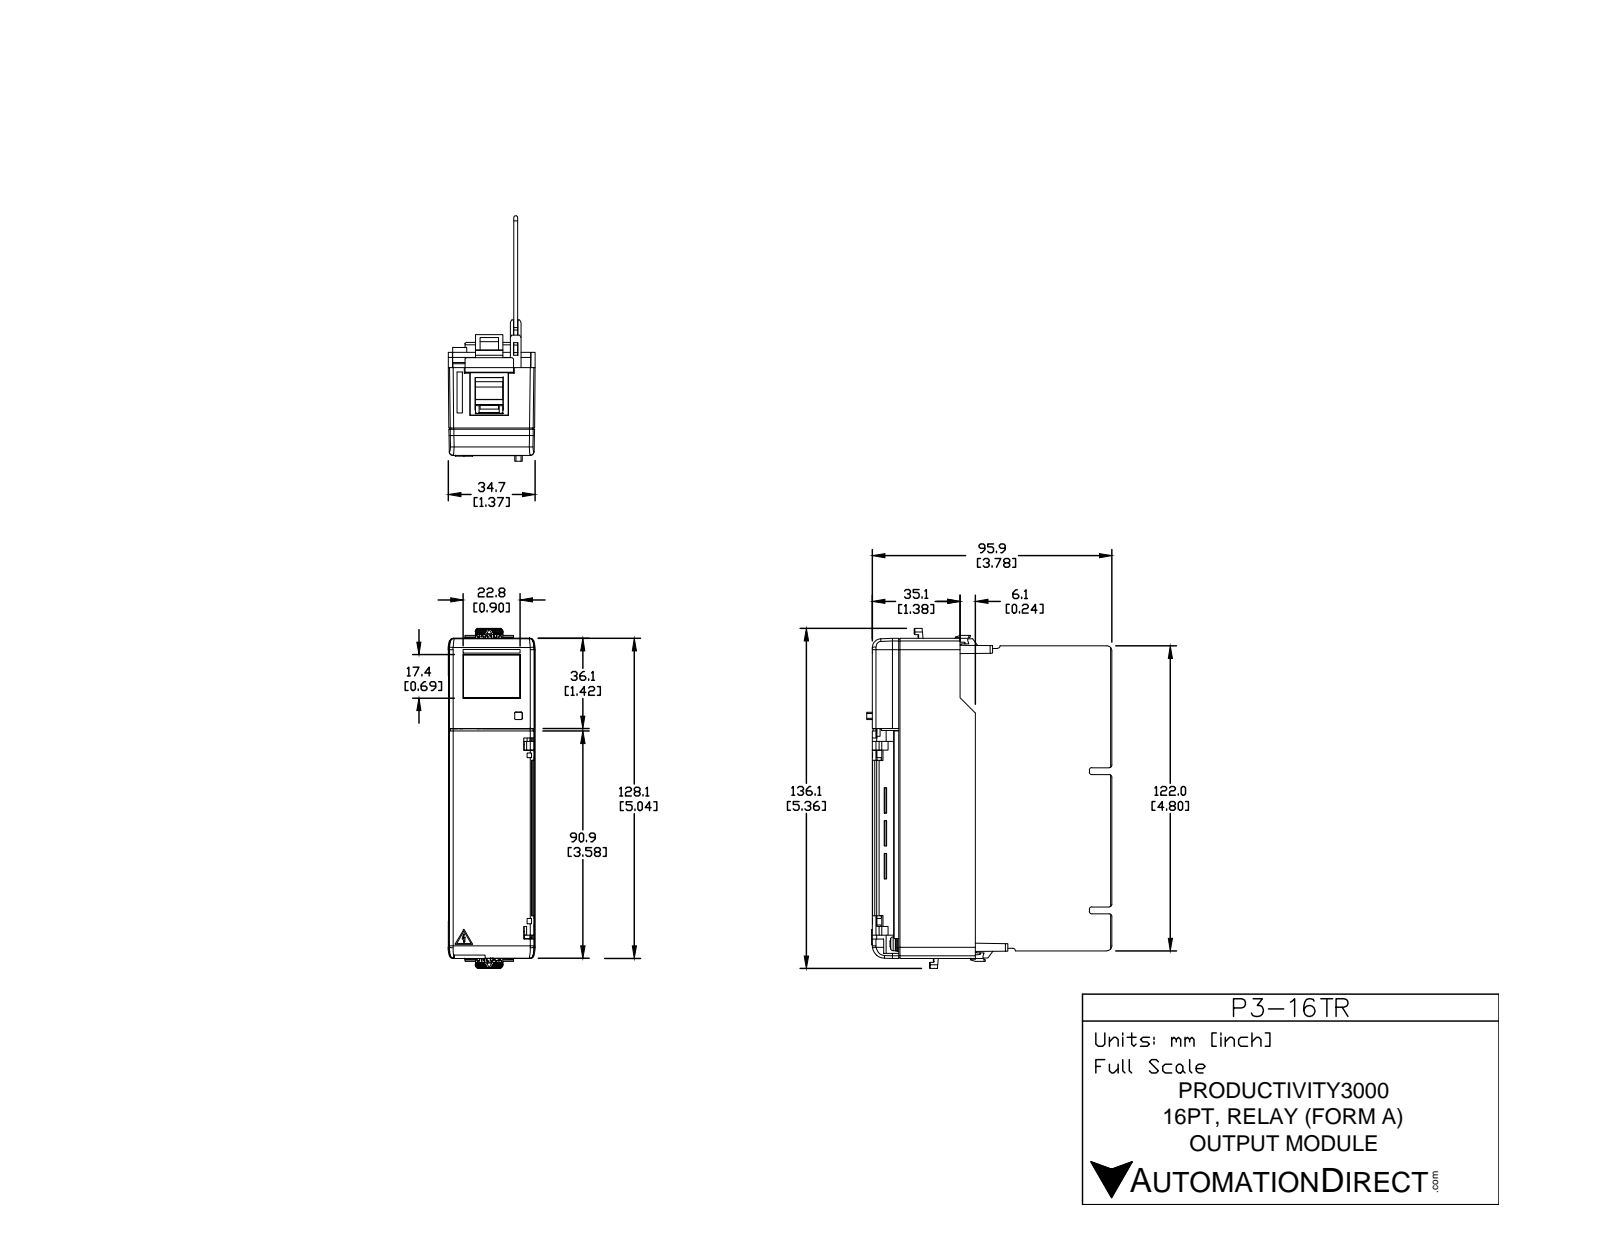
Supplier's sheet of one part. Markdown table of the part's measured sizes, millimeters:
| quantity | value |
| --- | --- |
| part name | P3-16TR |
| STEP written by | SolidWorks 2009 (CONFIG_CONTROL_DESIGN) |
| units | millimeters |
| bodies | 1 solid, 3804 faces (2821 planar, 737 cylindrical, 246 other) |
| overall size | 136.08 × 96.19 × 34.8 |
| volume | 101 334 mm³ |
| surface area | 75 406 mm² |
| round holes (diameter × count) | 3.2 × 22, 5 × 2, 1.8 × 1 |
| round bosses / shafts (diameter × count) | 5.5 × 22, 3 × 22, 2.4 × 20, 5.6 × 2, 2.2 × 2, 2 × 2, 1.5 × 1 |
| partial cylindrical surfaces (radius × count) | 0.5 × 91, 1 × 33, 0.3 × 29, 1.67 × 22, 1.5 × 13, 2 × 6, 0.2 × 5, 0.1 × 4 |
| main face-to-face distances | 1.6, 1.7, 28.23, 26.53, 32.56, 22.2, 2.2, 7.9, 6.8, 5.32 |
| hole center spacings | 8.68, 7.62, 13.84, 15.24, 20.59, 22.86, 27.79, 30.48 |
